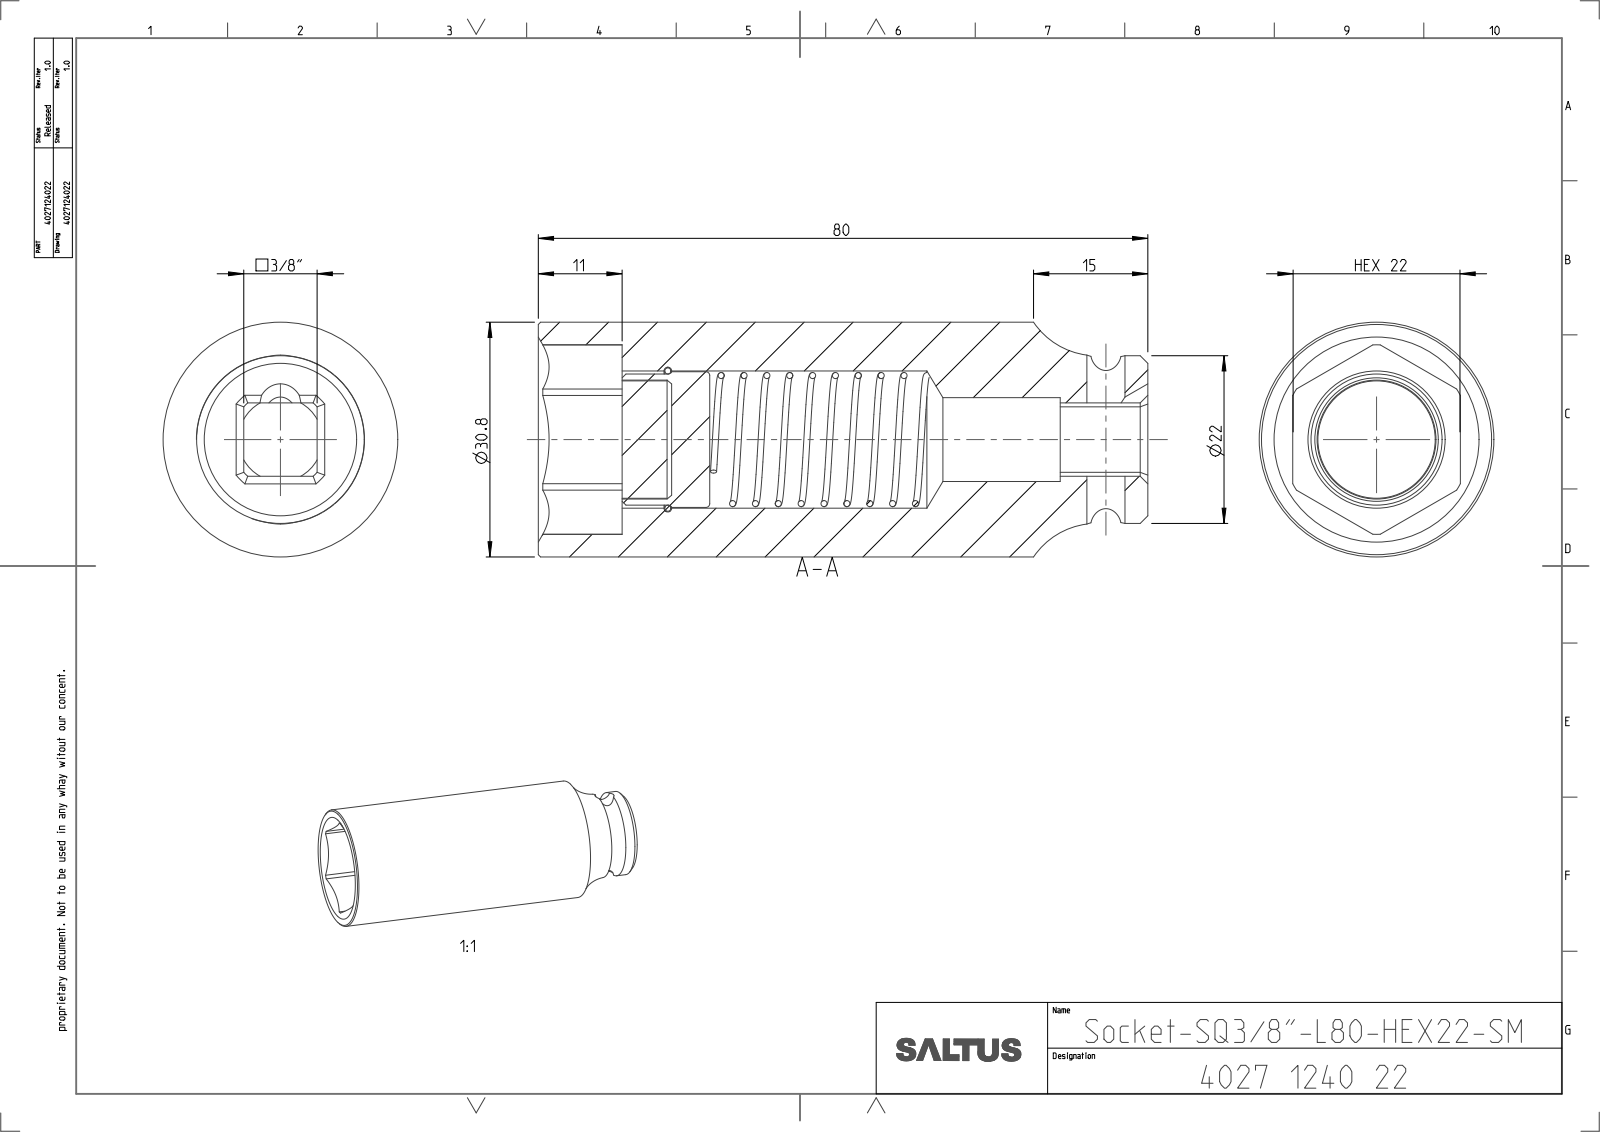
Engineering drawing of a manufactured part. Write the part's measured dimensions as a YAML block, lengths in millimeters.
part_name: "4027124022"
step_written_by: "CREO PARAMETRIC BY PTC INC, 2022414 (CONFIG_CONTROL_DESIGN)"
units: millimeters
bodies: {solids: 4, faces: 102, planar: 33, cylindrical: 33, other: 36}
overall_size: [80, 30.8, 30.8]
volume: 39509
surface_area: 16029
round_holes:
  - {diameter: 5, count: 1}
  - {diameter: 11, count: 1}
  - {diameter: 15.6, count: 1}
  - {diameter: 18, count: 1}
round_bosses_or_shafts:
  - {diameter: 30.8, count: 1}
  - {diameter: 22, count: 1}
  - {diameter: 17.8, count: 1}
  - {diameter: 17.2, count: 1}
  - {diameter: 15.4, count: 1}
partial_cylinders:
  - {radius: 3, count: 1}
  - {radius: 6.45, count: 1}
  - {radius: 12.43, count: 1}
face_to_face_distances: [22, 11.5, 57.5, 5.6, 5.9, 6.19, 15.81, 63.1, 69, 62.5]
